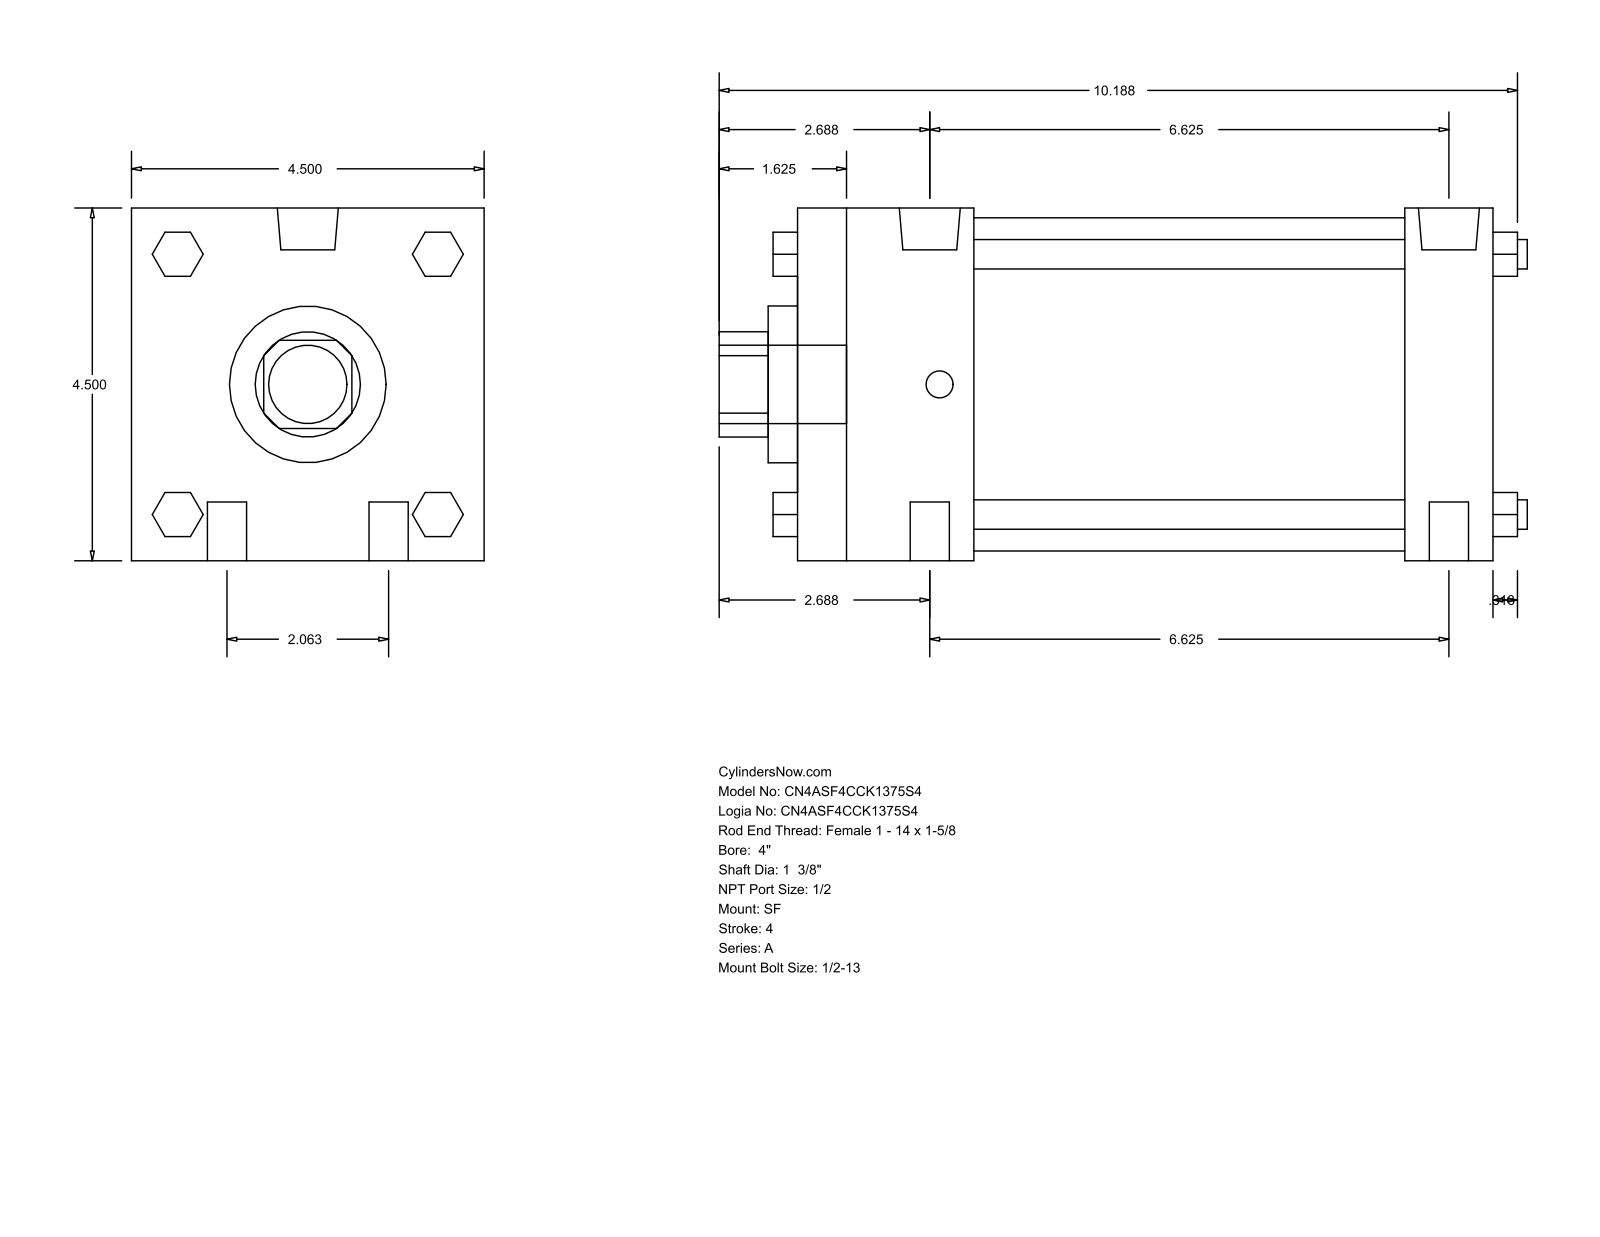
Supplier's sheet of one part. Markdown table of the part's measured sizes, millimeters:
| quantity | value |
| --- | --- |
| part name | A_SF__0400_1.375 |
| STEP written by | GSSL Pune (CONFIG_CONTROL_DESIGN) |
| units | millimeters |
| bodies | 0 solids, 124 faces (94 planar, 30 cylindrical, 0 other) |
| overall size | 261.94 × 114.3 × 114.3 |
| round holes (diameter × count) | 34.92 × 1, 50.8 × 1, 107.95 × 1 |
| round bosses / shafts (diameter × count) | 12.7 × 4, 9.53 × 4, 19.77 × 2, 8.73 × 2, 25.4 × 1 |
| partial cylindrical surfaces (radius × count) | 17.06 × 1 |
| main face-to-face distances | 114.3, 225.42, 28.57, 196.85, 57.15, 139.7, 168.27, 14.29, 9.52, 66.67 |
